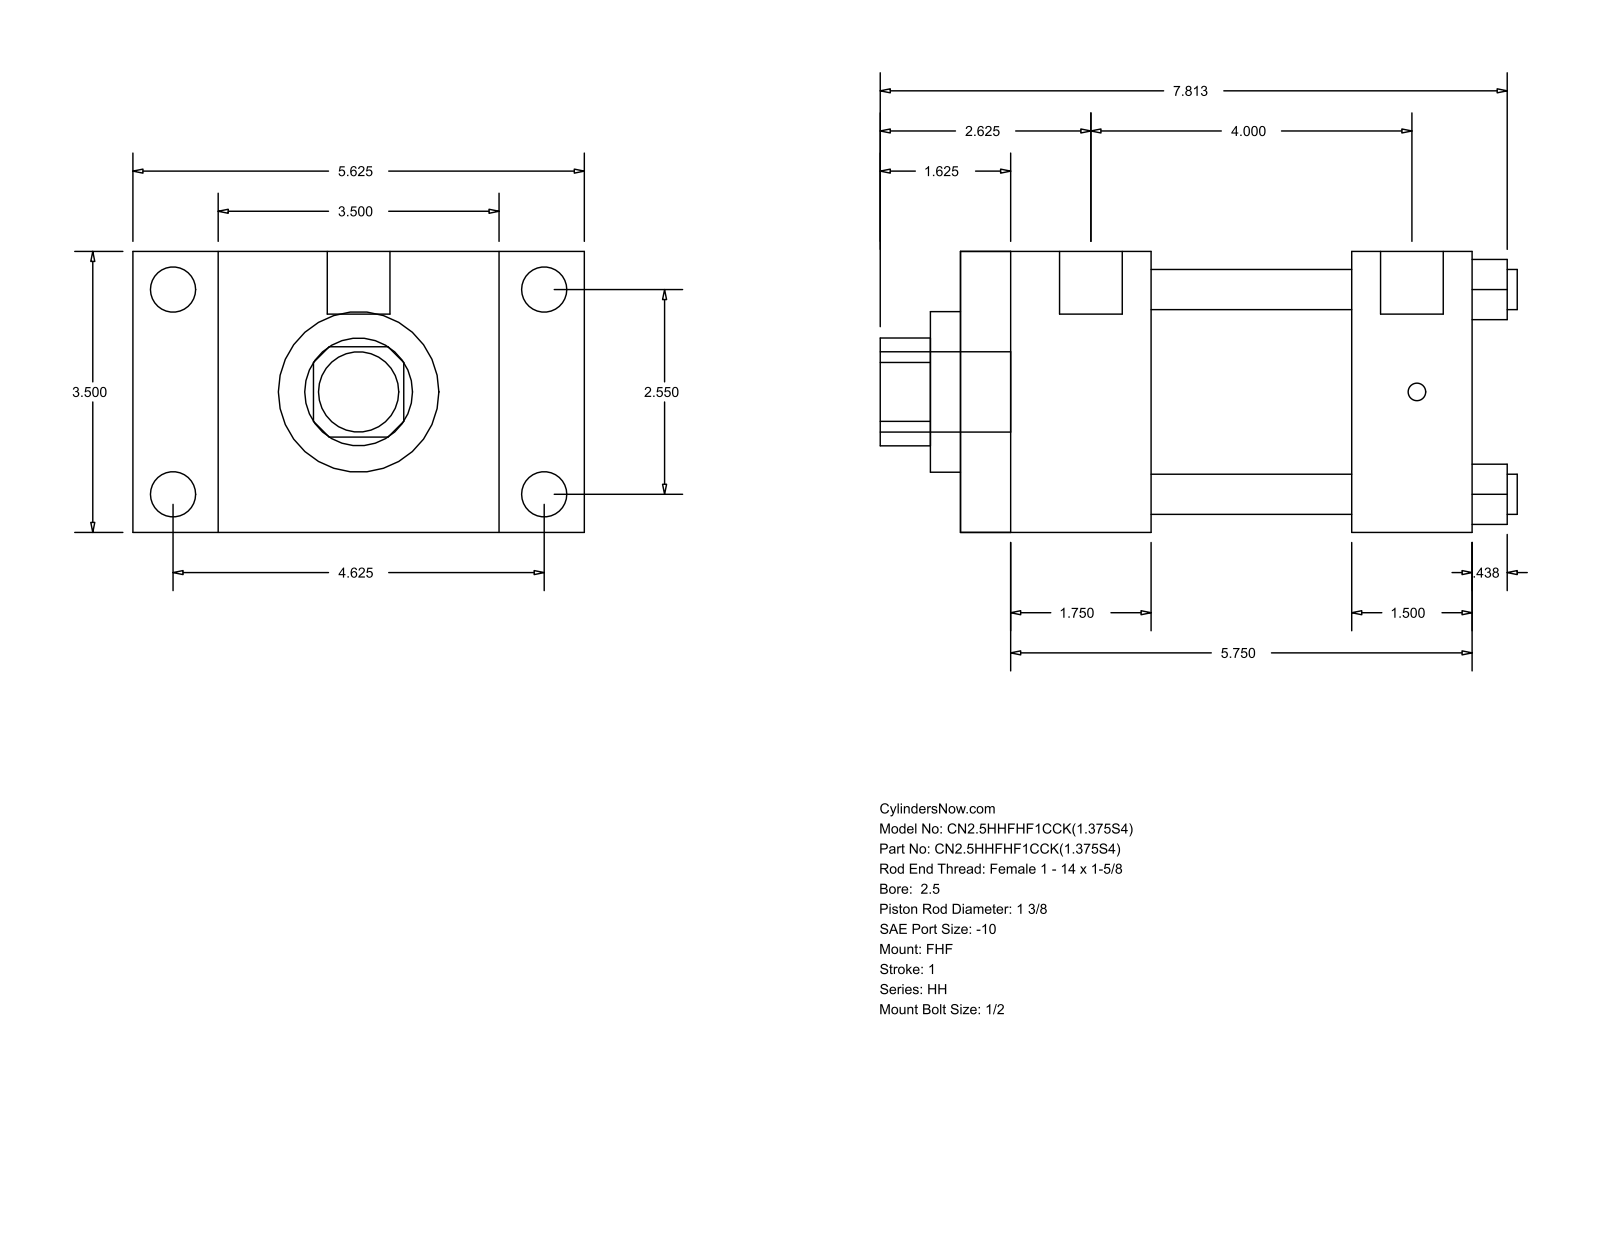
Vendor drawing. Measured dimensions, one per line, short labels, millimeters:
name: HH_FHF__0250_1.375
written by: GSSL Pune (CONFIG_CONTROL_DESIGN)
unit: mm
bodies: 0 solids, 88 faces (60 planar, 28 cylindrical, 0 other)
size: 201.61 × 142.88 × 88.9
holes: 4× ⌀12.7, 1× ⌀34.92, 1× ⌀50.8, 1× ⌀73.03
bosses: 4× ⌀14.3, 4× ⌀5.56, 2× ⌀19.84, 1× ⌀25.4
rounds: 1× R17.06
face distances: 88.9, 60.32, 115.89, 26.99, 161.92, 101.6, 142.88, 123.82, 63.5, 38.1
hole spacings: 45.79, 64.76, 91.58
